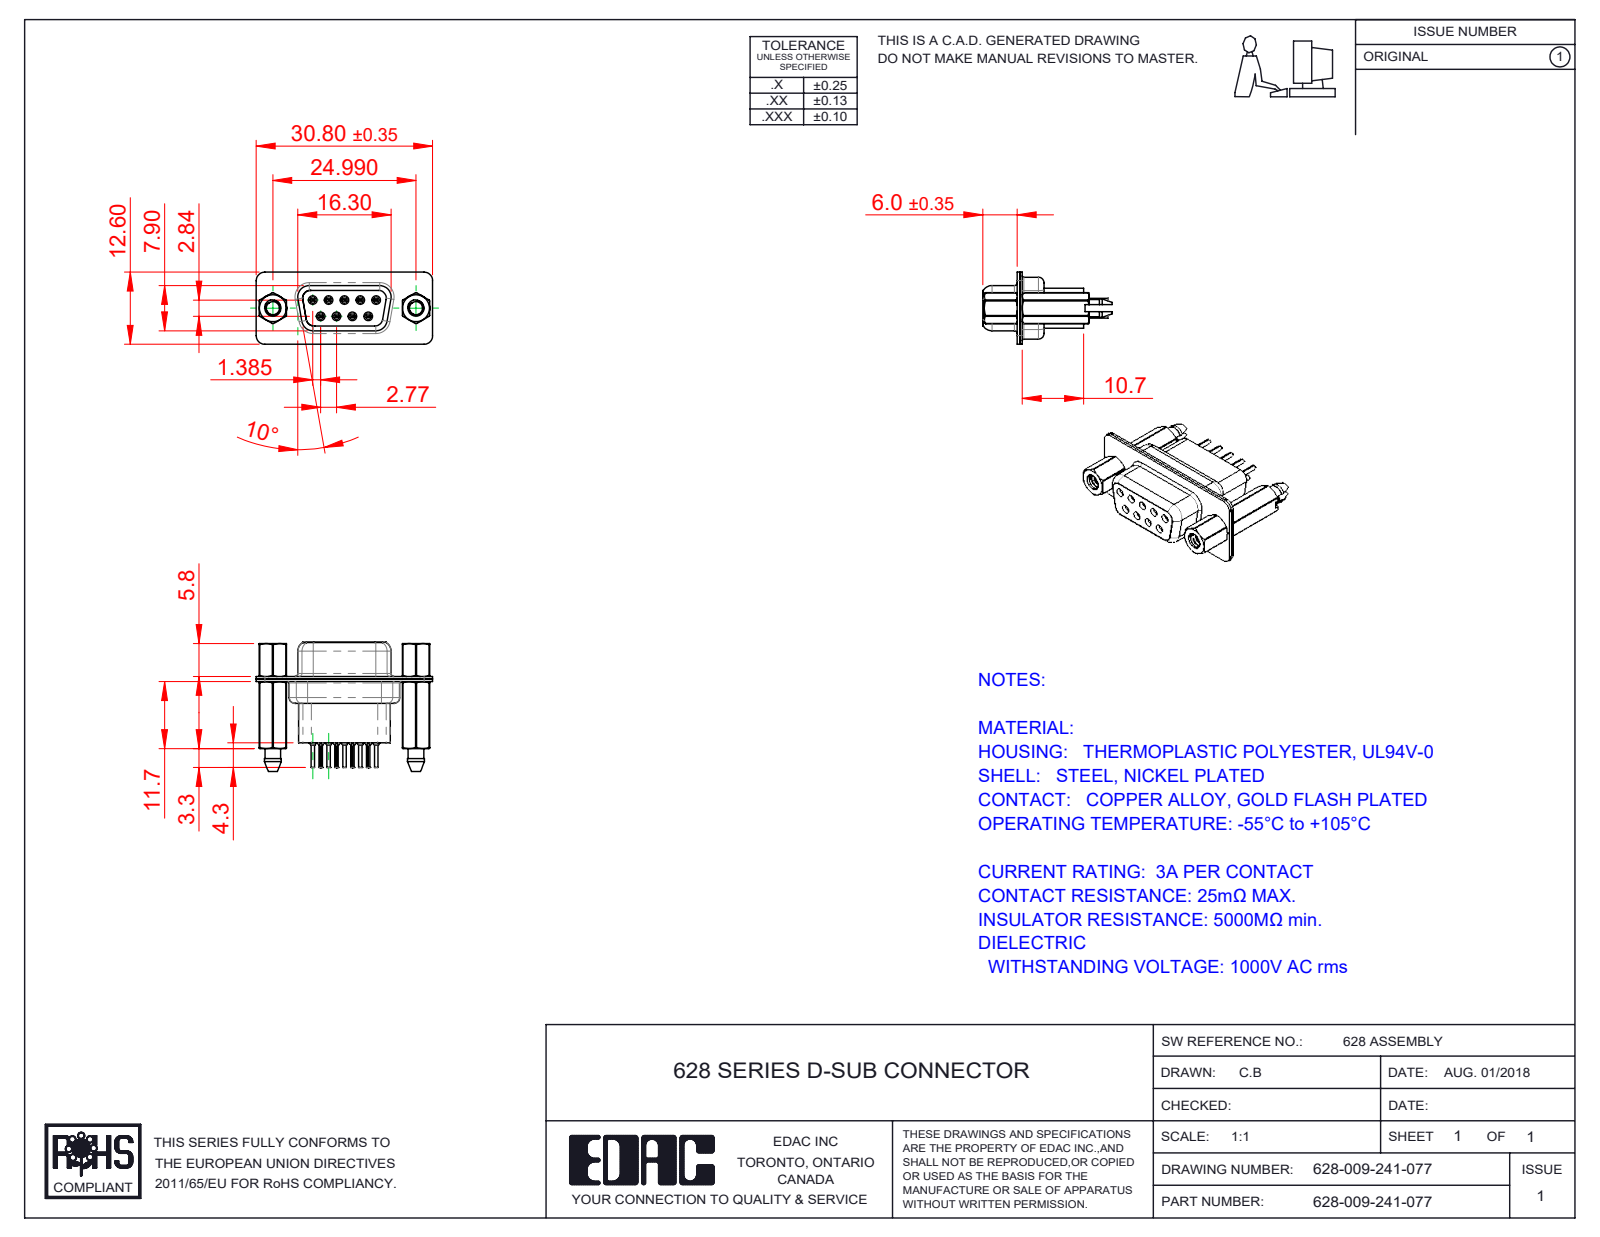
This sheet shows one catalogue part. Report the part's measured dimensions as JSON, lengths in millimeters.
{"part_name": "628 Housing_09 HP; 628 Shell Front_09 Contacts; 628 4-40 Hex Standoff; 628 4-40 Threaded Boardlock_HP41 (+4 more)", "step_written_by": "SolidWorks 2020 (CONFIG_CONTROL_DESIGN)", "units": "millimeters", "bodies": {"solids": 16, "faces": 1586, "planar": 400, "cylindrical": 538, "other": 648}, "overall_size": [30.8, 22.6, 12.6], "volume_mm3": 2737, "surface_area_mm2": 6376, "round_holes": [[0.2, 9], [0.8, 9], [0.9, 9], [1.1, 9], [1.6, 9], [1.7, 5], [2.26, 2], [2.29, 2], [4, 2], [4.05, 2], [4.85, 2]], "round_bosses_or_shafts": [[2, 9], [1.5, 9], [1.2, 9], [0.6, 9], [4.95, 2], [4.8, 2], [2.79, 2]], "partial_cylinders_radius": [[1.5, 19], [0.1, 18], [2, 12], [0.28, 9], [1.35, 6], [1.6, 6], [0.25, 4], [0.5, 4]], "face_to_face_distances": [0.45, 0.4, 0.9, 8.5, 4.76, 6.6, 1.9, 1.4, 7, 0.5], "hole_center_spacings": [3.16, 2.77, 5.54, 5.03, 5.04, 8.31, 7.48, 7.49]}
